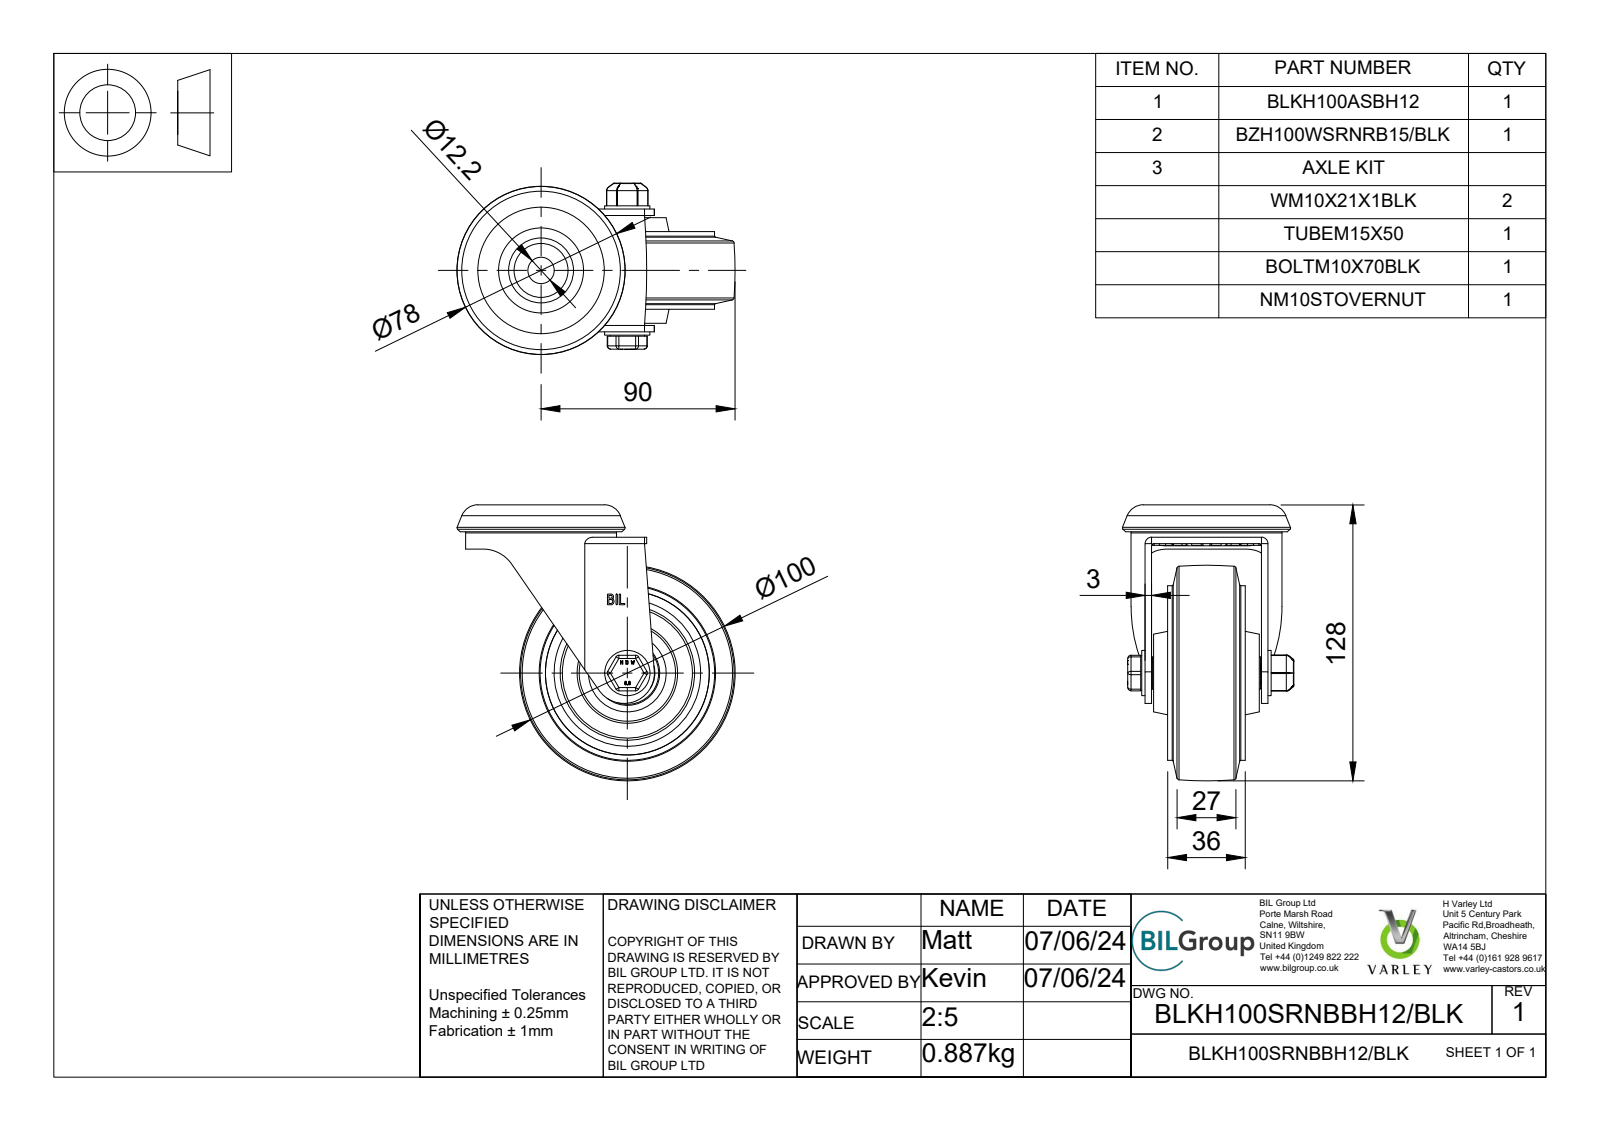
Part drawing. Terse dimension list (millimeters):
name: BLKH100SRNBBH12/BLK v3; BLKH100ASBH12 v1; BLACK PAINTED, PRESSED STEEL TOP HEAD; BLACK PAINTED, PRESSED STEEL TOP HEAD Geometry (+8 more)
written by: Autodesk Translation Framework v13.14.0.145 (AUTOMOTIVE_DESIGN)
unit: mm
bodies: 19 solids, 519 faces (273 planar, 132 cylindrical, 114 other)
size: 129 × 128 × 79.5
volume: 279 129 mm³; area: 122 480 mm²
holes: 2× ⌀30, 1× ⌀10, 1× ⌀10.2, 1× ⌀10.5, 1× ⌀12.2, 1× ⌀15, 1× ⌀22.5, 1× ⌀23, 1× ⌀64, 1× ⌀76
bosses: 8× ⌀4, 1× ⌀81, 1× ⌀70, 1× ⌀53.5, 1× ⌀28.75, 1× ⌀25, 1× ⌀22.75, 1× ⌀21
rounds: 12× R1.5, 6× R0.5, 4× R0.23, 4× R0.45, 3× R1.25, 2× R0.44, 2× R0.45, 2× R3
face distances: 3, 54, 10.5, 2, 46.5, 15, 7.5, 43.5, 8, 13
